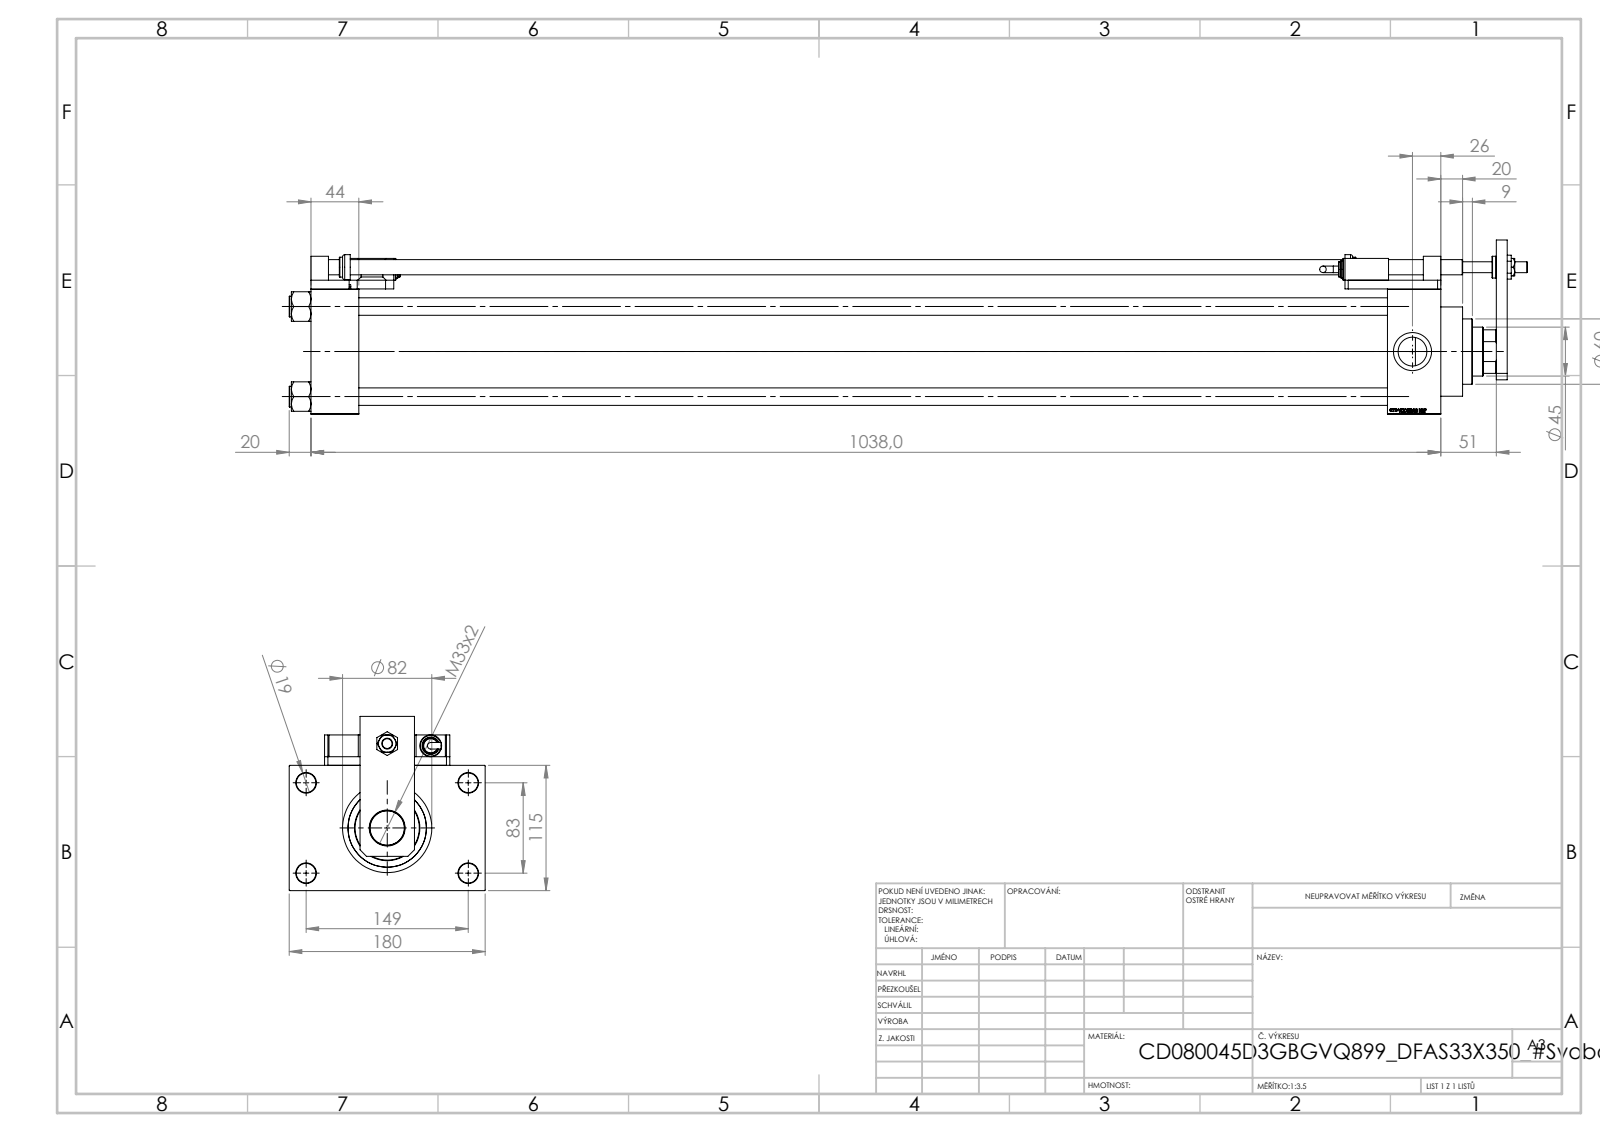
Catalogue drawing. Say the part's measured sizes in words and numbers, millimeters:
The part is named "V215CD_SWITCH_Q_TYC; V215CD_SWITCH_Q_DIMA; V215CD_D_Body; V215CD_SWITCH_Q_NUT (+8 more)". Its 3-D file was written by "SolidWorks 2019 (CONFIG_CONTROL_DESIGN)". It is 26 solids with 1480 faces: 714 planar, 167 cylindrical and 599 other. Overall it measures 1137.5 by 180 by 160 millimeters. Its volume is 5 210 000 cubic millimeters and its surface area 1 198 000 square millimeters. Round holes: 4 of diameter 8.5, 4 of diameter 13.5, 4 of diameter 16, 4 of diameter 18, 4 of diameter 26.44, 4 of diameter 35, 3 of diameter 7, 1 of diameter 10, 1 of diameter 14, 1 of diameter 31.5, 1 of diameter 33, 1 of diameter 45. Round bosses or shafts: 4 of diameter 19, 3 of diameter 20, 2 of diameter 16, 2 of diameter 14, 2 of diameter 6, 1 of diameter 86, 1 of diameter 82, 1 of diameter 60. Partial cylindrical surfaces (rounded edges, fillets, slot ends): 4 of radius 7.5, 1 of radius 22. The main face-to-face distances are 115, 8, 49, 44, 994, 1038, 989, 945, 123, 32.5. The hole center spacings are 33.15, 58.48, 82.7, 85.28, 89.24, 115.85, 142.43, 21.26.
